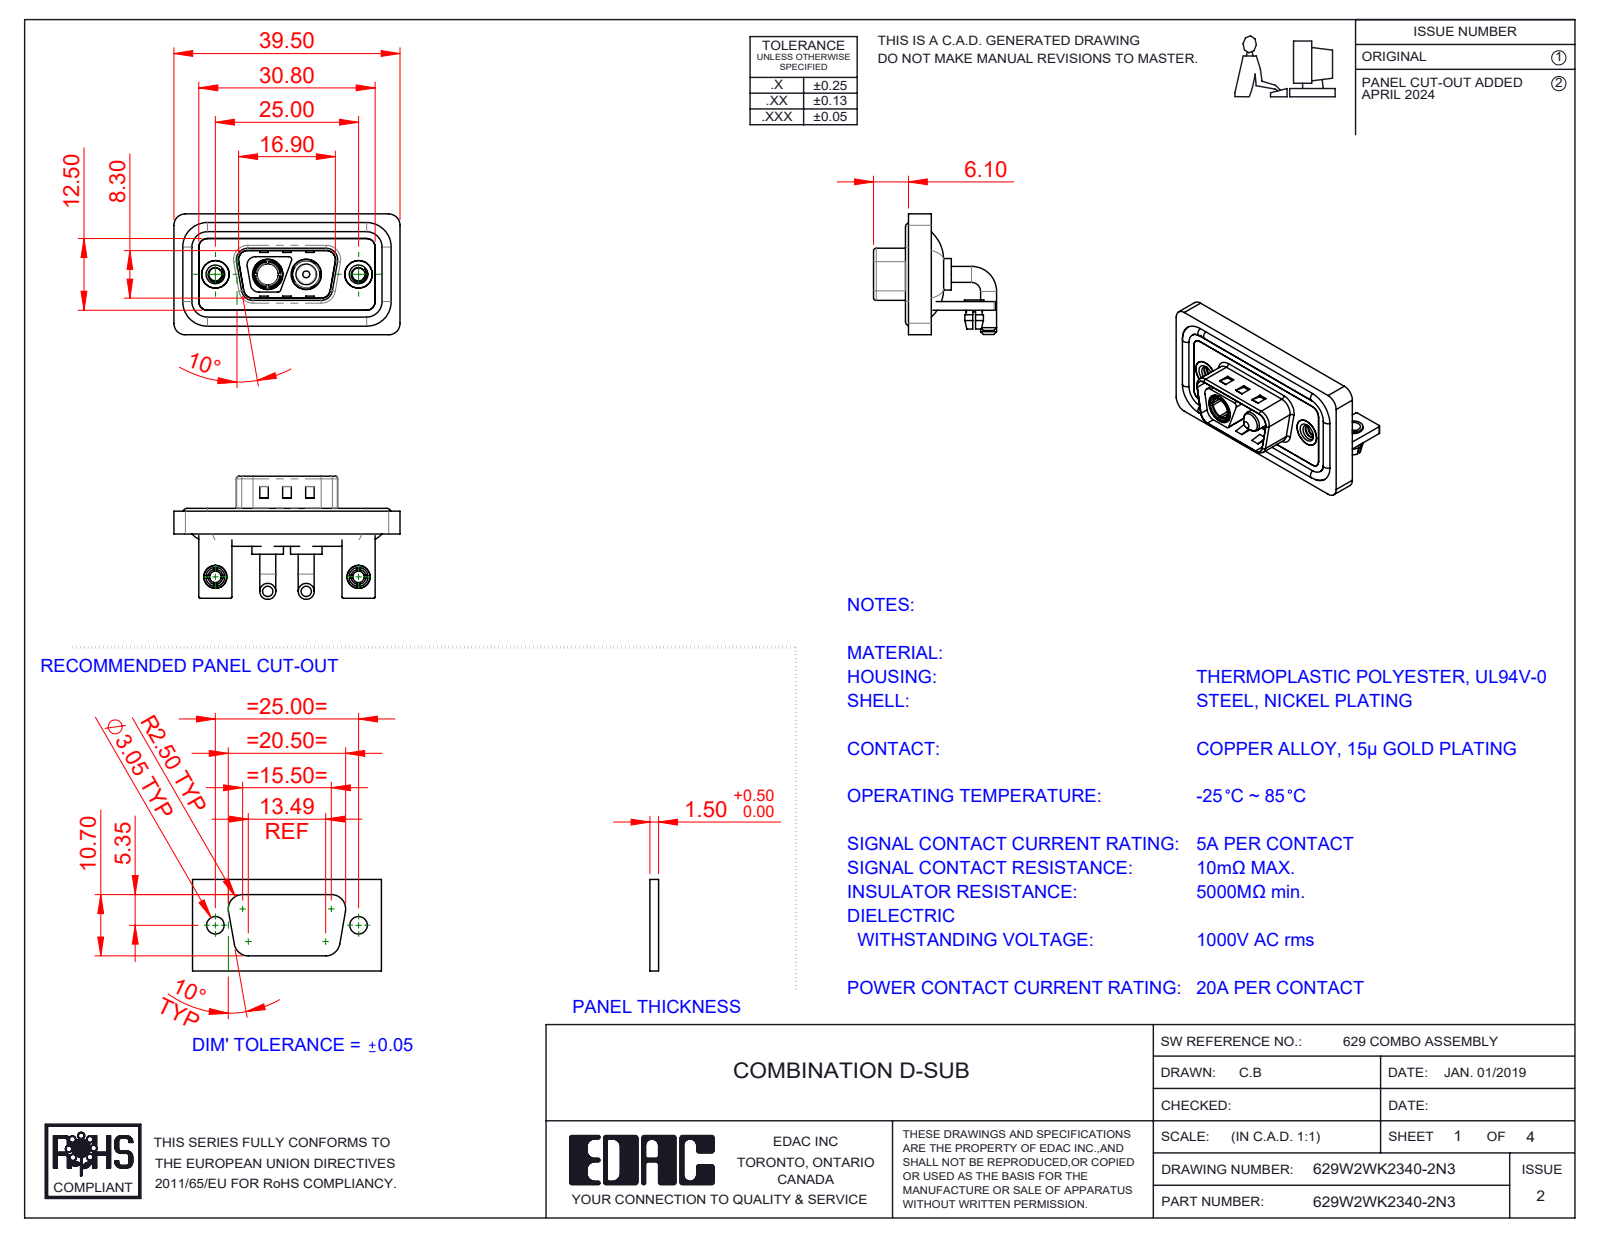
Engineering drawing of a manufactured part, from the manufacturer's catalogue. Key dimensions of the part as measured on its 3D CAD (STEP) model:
Part name (STEP PRODUCT): 629Combo Waterproof Housing_09 Contacts; 629Combo Housing_2WK2; 629Combo Board Lock; 629Combo Stabilizer Bracket (+6 more)
STEP written by: SolidWorks 2023 (CONFIG_CONTROL_DESIGN)
Units: millimetres
Bodies: 15 solids, 674 faces (257 planar, 281 cylindrical, 136 other)
Overall size (bounding box): 39.5 × 21.5 × 21.1
Volume: 4 996 mm³ · Surface area: 8 329 mm²
Round holes (diameter × count): ⌀2 ×2, ⌀2.26 ×2, ⌀2.5 ×2, ⌀3.2 ×2, ⌀4 ×2, ⌀4.8 ×2, ⌀4.85 ×2, ⌀5 ×2, ⌀5.3 ×2, ⌀3.7 ×1
Round bosses / shafts (diameter × count): ⌀2.8 ×4, ⌀1.6 ×4, ⌀5.5 ×2, ⌀5.2 ×2, ⌀4.9 ×2, ⌀4.75 ×2, ⌀4 ×2, ⌀3.75 ×2
Partial cylindrical surfaces — rounded edges, fillets, slot ends (radius × count): R1.5 ×20, R2 ×19, R0.25 ×16, R0.5 ×11, R1.6 ×8, R0.6 ×4, R0.65 ×4, R0.9 ×4
Main face-to-face distances: 0.4, 1.5, 2.9, 0.8, 1.1, 1.2, 2.1, 1.6, 3.7, 2.5
Hole centre spacings: 9.14, 15.86, 25, 6.72
